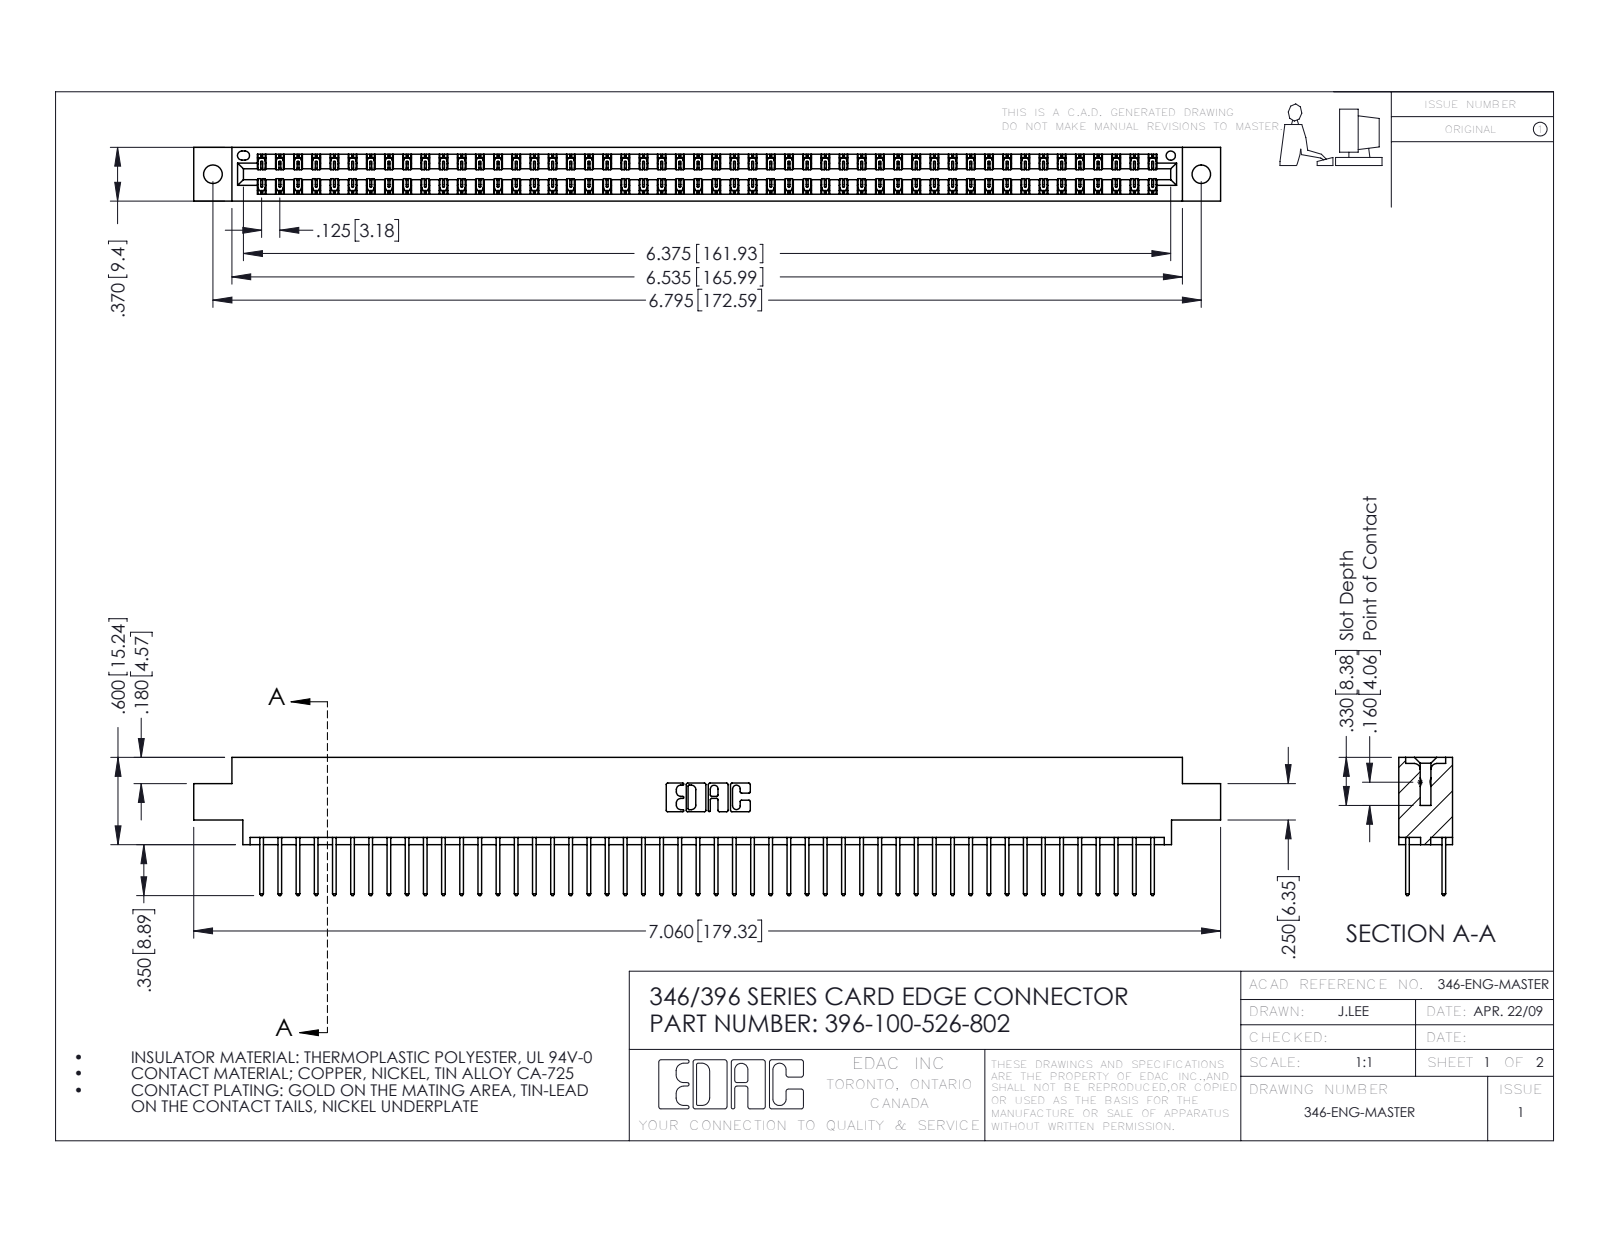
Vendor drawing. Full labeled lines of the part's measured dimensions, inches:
Part name (STEP PRODUCT): 345-292-001_345-293-126; 346 Part_0.170 Offset - 0.128 Dia; 396-100-526-802
STEP written by: SolidWorks 2016 (CONFIG_CONTROL_DESIGN)
Units: inches
Bodies: 101 solids, 5326 faces (3580 planar, 1746 cylindrical, 0 other)
Overall size (bounding box): 7.06 × 0.95 × 0.37
Volume: 1.069 in³ · Surface area: 38.52 in²
Round holes (diameter × count): ⌀0.128 ×2, ⌀0.064 ×1
Partial cylindrical surfaces — rounded edges, fillets, slot ends (radius × count): R0.006 ×150, R0.01 ×100, R0.01 ×22, R0.007 ×6, R0.031 ×6, R0.026 ×3, R0.014 ×2, R0.022 ×2
Main face-to-face distances: 0.048, 0.322, 0.25, 0.37, 0.072, 0.298, 0.025, 0.275, 0.148, 0.222
Hole centre spacings: 0.246, 6.586, 6.795
